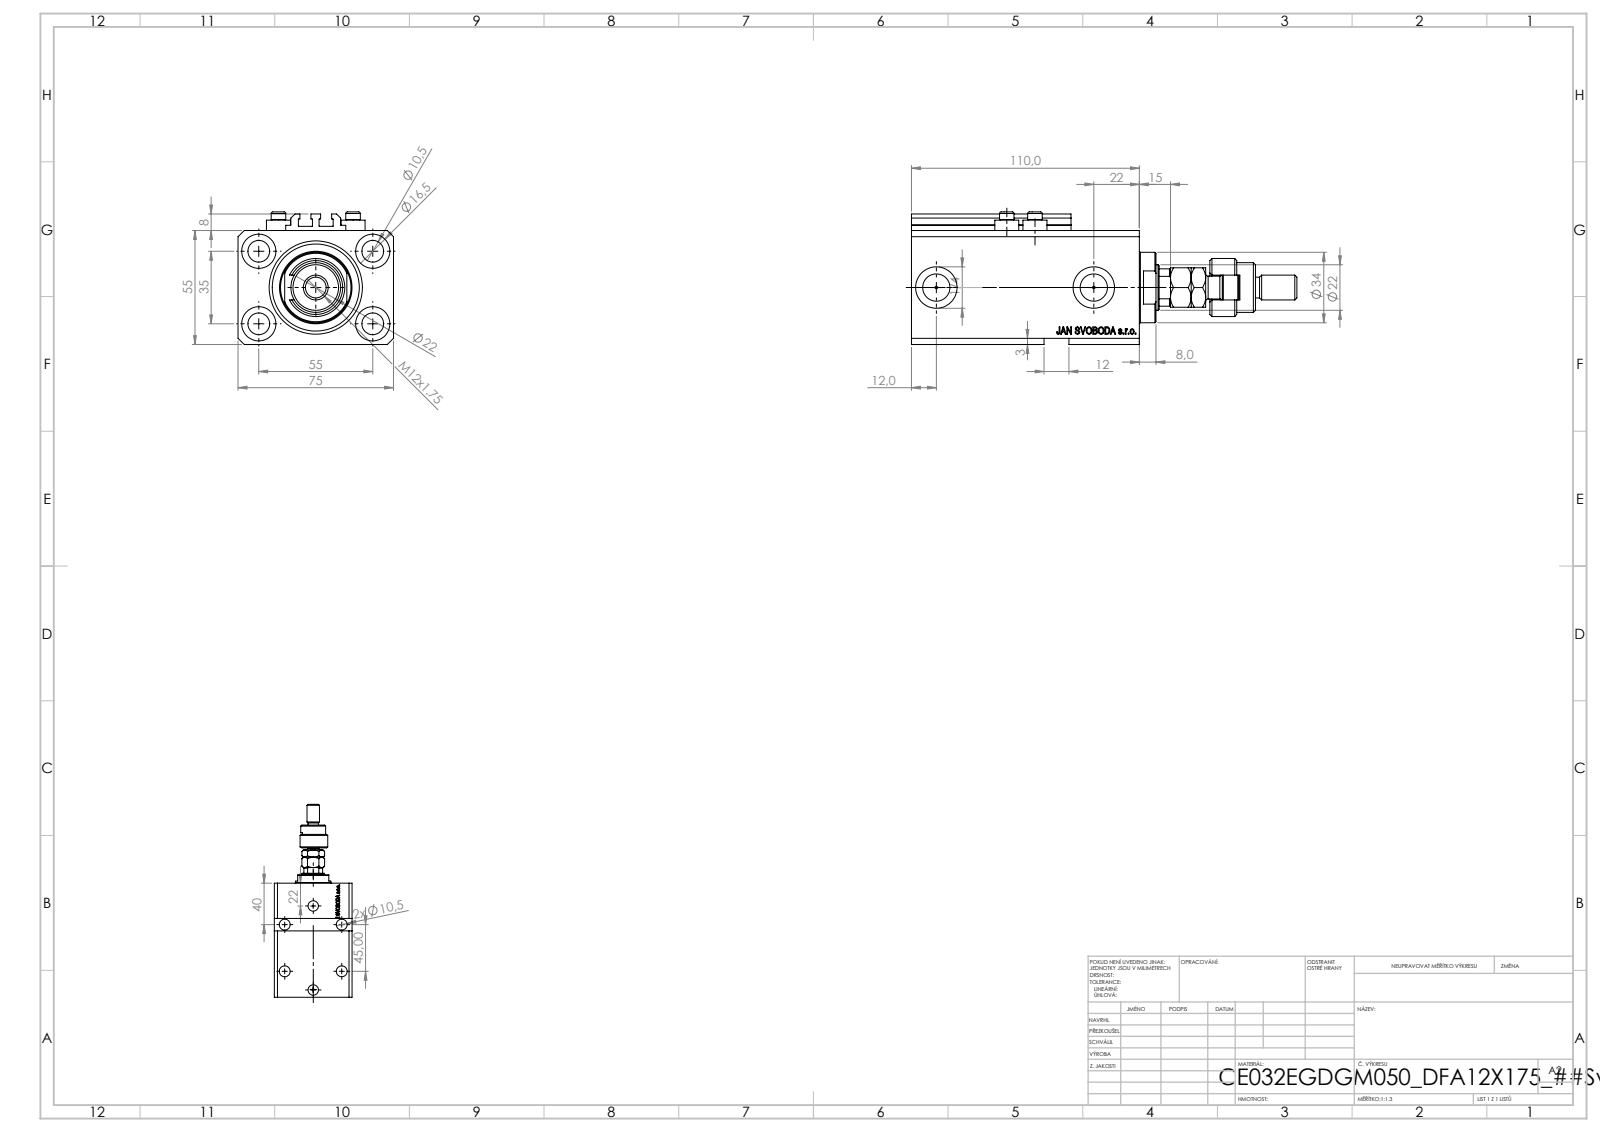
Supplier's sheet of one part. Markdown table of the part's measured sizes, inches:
| quantity | value |
| --- | --- |
| part name | V250CE_E_Body; FEMALE_PART_FOR_DFA; ALLEN BOLT V250CE; MFA (+2 more) |
| STEP written by | SolidWorks 2019 (CONFIG_CONTROL_DESIGN) |
| units | inches |
| bodies | 10 solids, 1185 faces (546 planar, 171 cylindrical, 468 other) |
| overall size | 7.323 × 2.953 × 2.52 |
| volume | 24.14 in³ |
| surface area | 161.1 in² |
| round holes (diameter × count) | 0.413 × 9, 0.049 × 4, 0.157 × 4, 0.65 × 4, 0.394 × 2, 0.518 × 2, 0.787 × 2, 0.866 × 1, 1.26 × 1, 1.772 × 1 |
| round bosses / shafts (diameter × count) | 0.457 × 4, 0.276 × 4, 1.339 × 1, 1.102 × 1, 0.945 × 1, 0.709 × 1, 0.472 × 1, 0.433 × 1 |
| partial cylindrical surfaces (radius × count) | 0.008 × 10, 0.384 × 1, 0.413 × 1 |
| main face-to-face distances | 2.165, 2.953, 0.591, 4.331, 3.74, 0.39, 0.118, 0.315, 0.748, 3.35 |
| hole center spacings | 1.283, 1.294, 2.165, 2.706, 0.535, 0.555, 0.907, 1.016 |
